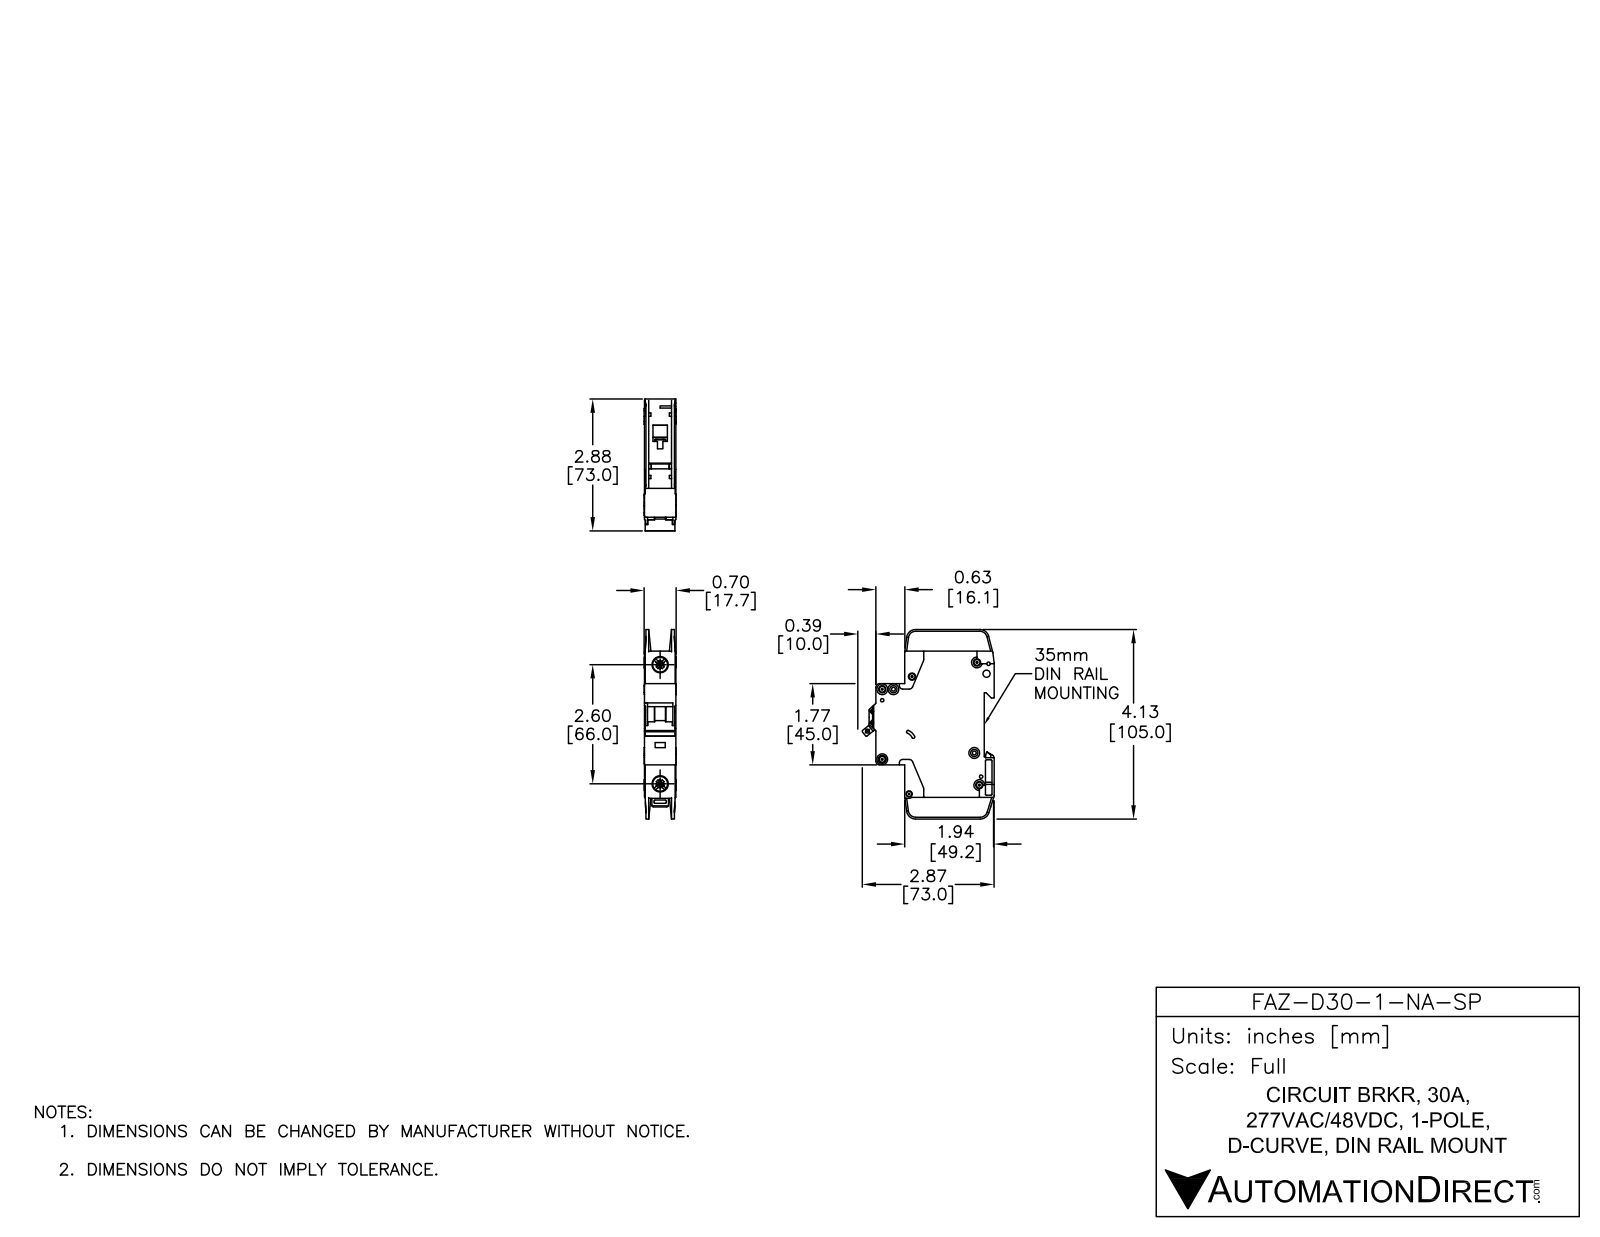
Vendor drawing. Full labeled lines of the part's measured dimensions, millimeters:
Part name (STEP PRODUCT): FAZ-D30-1-NA-SP
STEP written by: SolidWorks 2014 (AUTOMOTIVE_DESIGN)
Units: millimetres
Bodies: 3 solids, 784 faces (409 planar, 263 cylindrical, 112 other)
Overall size (bounding box): 105 × 73.04 × 17.7
Volume: 77 695 mm³ · Surface area: 24 740 mm²
Round holes (diameter × count): ⌀3.6 ×7, ⌀1.09 ×2, ⌀1.5 ×2, ⌀4 ×2, ⌀7.15 ×2, ⌀8.2 ×2, ⌀1.9 ×1, ⌀2.15 ×1, ⌀2.2 ×1, ⌀2.55 ×1, ⌀3.3 ×1, ⌀3.4 ×1
Round bosses / shafts (diameter × count): ⌀6 ×7, ⌀2.5 ×1
Partial cylindrical surfaces — rounded edges, fillets, slot ends (radius × count): R0.25 ×29, R0.5 ×18, R1 ×10, R2 ×10, R5 ×5, R4 ×4, R1.8 ×3, R0.2 ×2
Main face-to-face distances: 17.5, 15.05, 0.7, 2.45, 1.75, 15.75, 13.3, 14, 12.6, 2
Hole centre spacings: 6.2, 5.19, 6.1, 8.19, 8.56, 8.7, 11.11, 12.45
